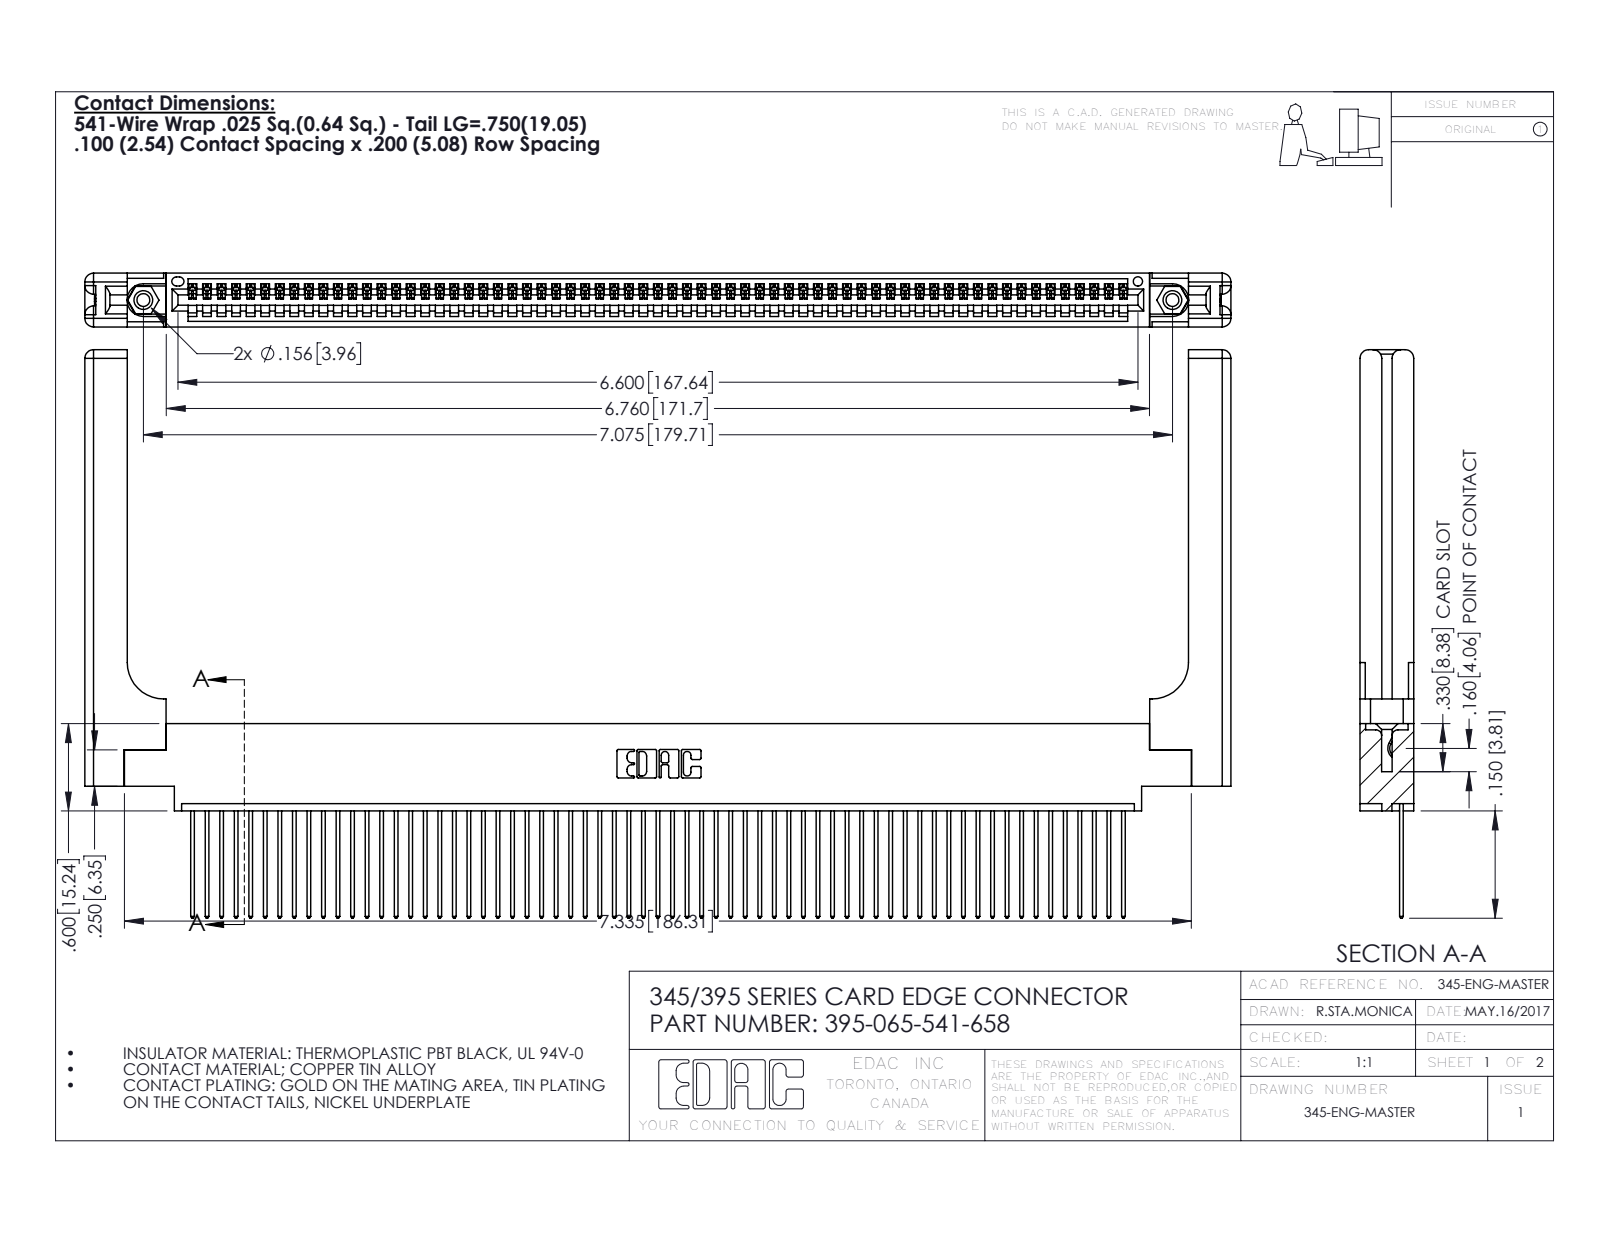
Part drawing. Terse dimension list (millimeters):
name: 395-065-541-658; 345-250-001_345-250-001-102; 345 Part_0.170 Offset - 0.156 Dia-TH; 345-292-001_345-293-141 (+1 more)
written by: SolidWorks 2016 (CONFIG_CONTROL_DESIGN)
unit: mm
bodies: 70 solids, 4156 faces (2832 planar, 1264 cylindrical, 60 other)
size: 200.1 × 99.2 × 9.4
volume: 27 810 mm³; area: 32 650 mm²
holes: 2× ⌀2.3, 2× ⌀3.2, 2× ⌀4, 1× ⌀1.6
bosses: 2× ⌀3.9
rounds: 130× R0.2, 130× R0.3, 22× R0.3, 16× R1.5, 6× R0.2, 6× R0.8, 3× R0.7, 2× R0.8
face distances: 1.8, 7.6, 9.4, 2.5, 6.9, 0.6, 5.1, 5.7, 3.8, 3.8
hole spacings: 6.9, 173.7, 179.7
